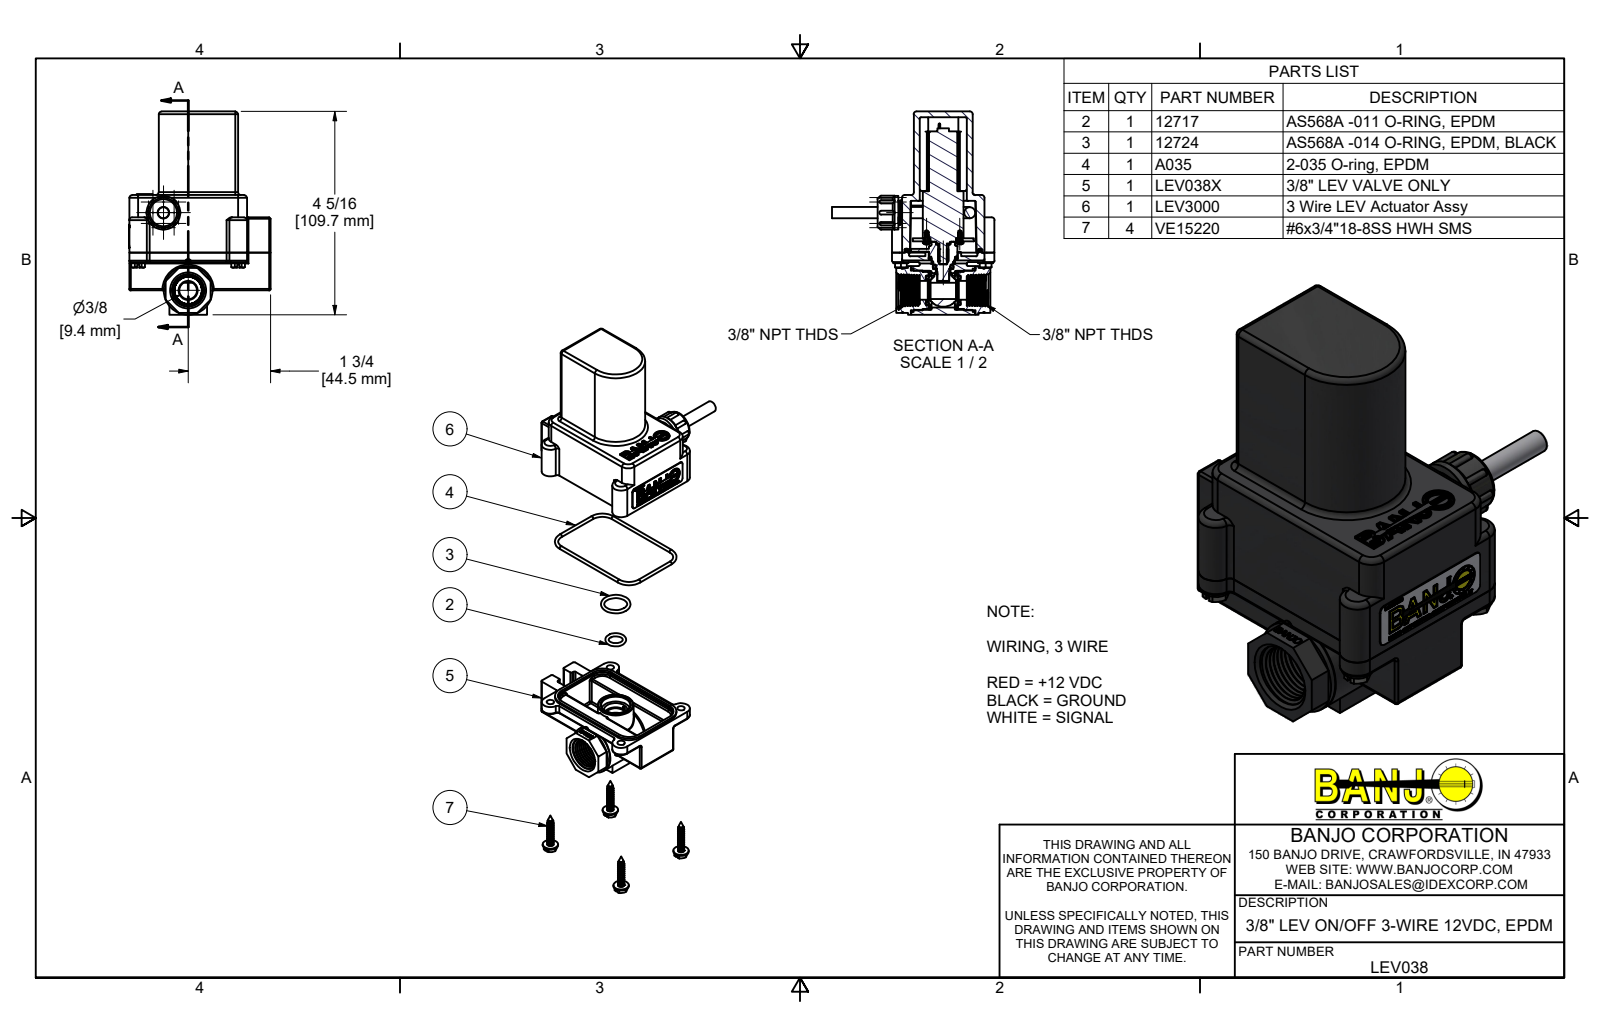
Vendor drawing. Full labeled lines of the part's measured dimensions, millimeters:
Part name (STEP PRODUCT): LEV038; LEV038X; LEV03254D; LEV03255PE (+8 more)
STEP written by: Autodesk Inventor 2022 (AUTOMOTIVE_DESIGN)
Units: millimetres
Bodies: 32 solids, 3207 faces (1506 planar, 681 cylindrical, 1020 other)
Overall size (bounding box): 109.7 × 87.7 × 76.5
Volume: 135 700 mm³ · Surface area: 89 740 mm²
Round holes (diameter × count): ⌀0.9 ×8, ⌀1.6 ×4, ⌀2.4 ×4, ⌀2.8 ×4, ⌀4.1 ×4, ⌀5.1 ×4, ⌀1.2 ×2, ⌀1.4 ×2, ⌀5.8 ×2, ⌀8.2 ×2, ⌀1.6 ×1, ⌀4.3 ×1
Round bosses / shafts (diameter × count): ⌀8.3 ×4, ⌀4 ×4, ⌀3.5 ×4, ⌀2 ×4, ⌀1.8 ×4, ⌀1.5 ×4, ⌀1.2 ×4, ⌀8.6 ×2
Partial cylindrical surfaces — rounded edges, fillets, slot ends (radius × count): R0.8 ×102, R0.4 ×59, R1.5 ×22, R0.3 ×16, R3.2 ×10, R1 ×8, R4.7 ×8, R1.6 ×5
Main face-to-face distances: 3.2, 1.7, 34.9, 9.5, 25.4, 38.1, 28.6, 3.2, 6.4, 12.7
Hole centre spacings: 2.5, 12.7, 21.7, 24.1, 25.1, 3.6, 9, 9
